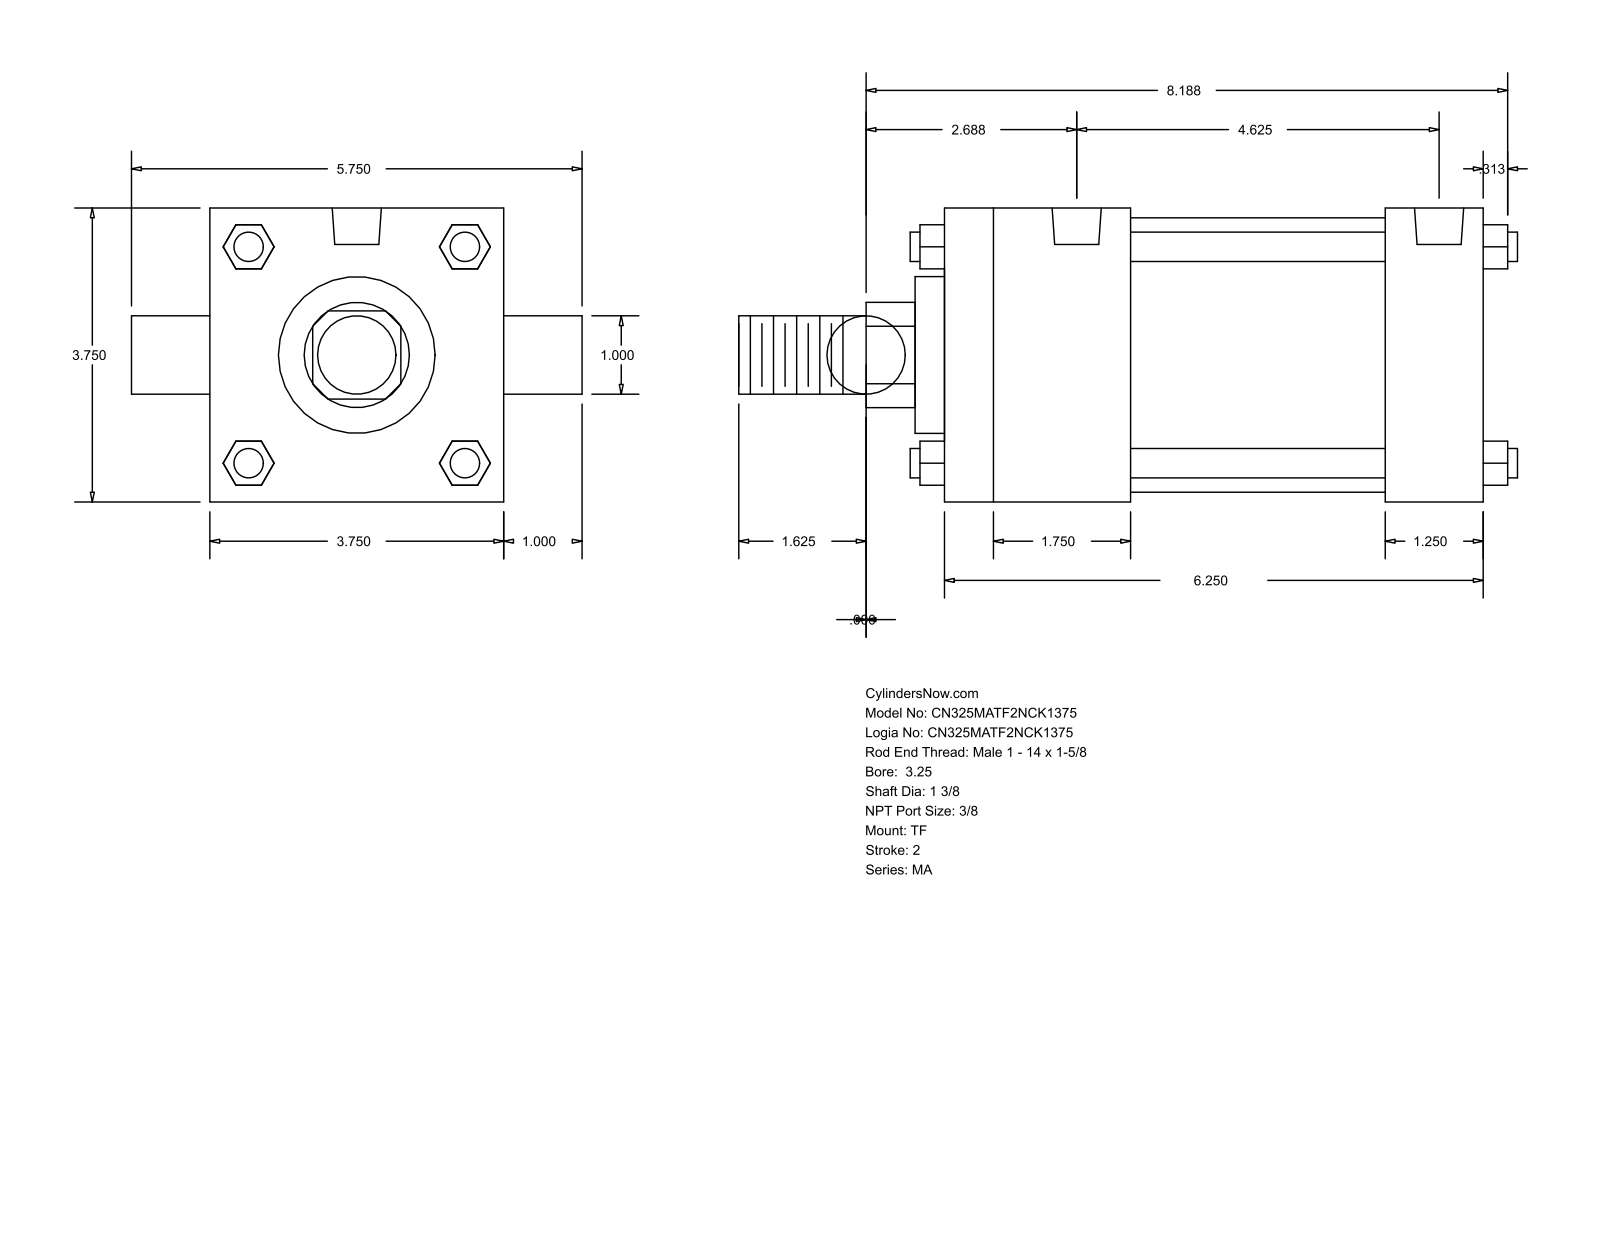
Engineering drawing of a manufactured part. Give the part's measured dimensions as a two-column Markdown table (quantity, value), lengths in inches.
| quantity | value |
| --- | --- |
| part name | MA_TF__0325_1.375 |
| STEP written by | GSSL Pune (CONFIG_CONTROL_DESIGN) |
| units | inches |
| bodies | 0 solids, 120 faces (92 planar, 28 cylindrical, 0 other) |
| overall size | 9.937 × 5.75 × 3.75 |
| round holes (diameter × count) | 0.437 × 3, 0.627 × 2 |
| round bosses / shafts (diameter × count) | 0.375 × 4, 1 × 2, 3.5 × 1, 2 × 1, 1.375 × 1 |
| partial cylindrical surfaces (radius × count) | 0.672 × 1 |
| main face-to-face distances | 3.75, 6.875, 2.375, 5.625, 3.25, 4.5, 1.25, 0.375, 2.75, 6 |
| hole center spacings | 0.188, 4.437, 4.25, 4.625 |
